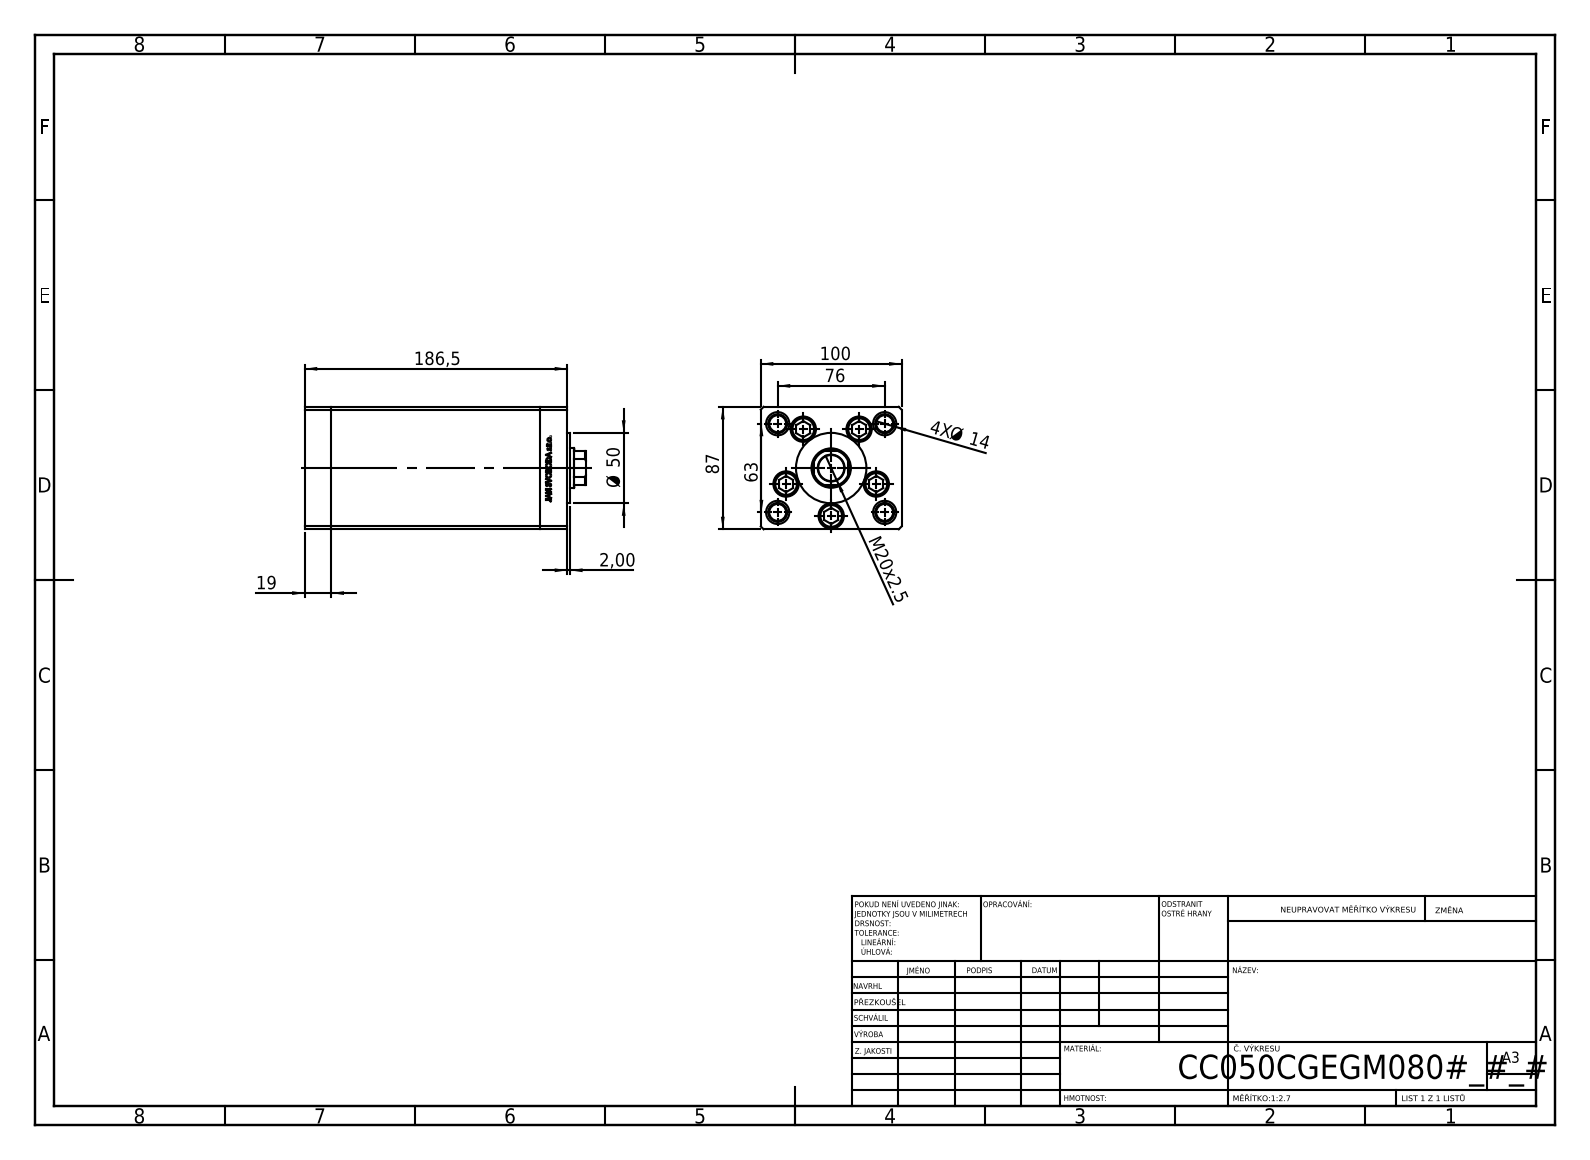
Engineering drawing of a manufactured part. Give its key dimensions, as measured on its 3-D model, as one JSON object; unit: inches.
{"part_name": "V220C BACK_C; V220C FRONT; ALLEN BOLT; V220C_VC_C (+1 more)", "step_written_by": "SolidWorks 2019 (CONFIG_CONTROL_DESIGN)", "units": "inches", "bodies": {"solids": 13, "faces": 1160, "planar": 538, "cylindrical": 160, "other": 462}, "overall_size": [7.854, 3.937, 3.425], "volume_in3": 81.47, "surface_area_in2": 354.3, "round_holes": [[0.531, 9], [0.709, 5], [0.472, 4], [0.65, 4], [0.669, 1], [0.728, 1], [1.102, 1]], "round_bosses_or_shafts": [[0.315, 5], [0.669, 4], [1.969, 1]], "partial_cylinders_radius": [[0.037, 2], [0.531, 1]], "face_to_face_distances": [3.937, 3.425, 0.748, 5.846, 6.594, 1.348, 7.343, 5.994, 5.246, 0.6], "hole_center_spacings": [1.339, 1.943, 0.732, 0.828, 1.499, 1.546, 1.607, 1.702]}
